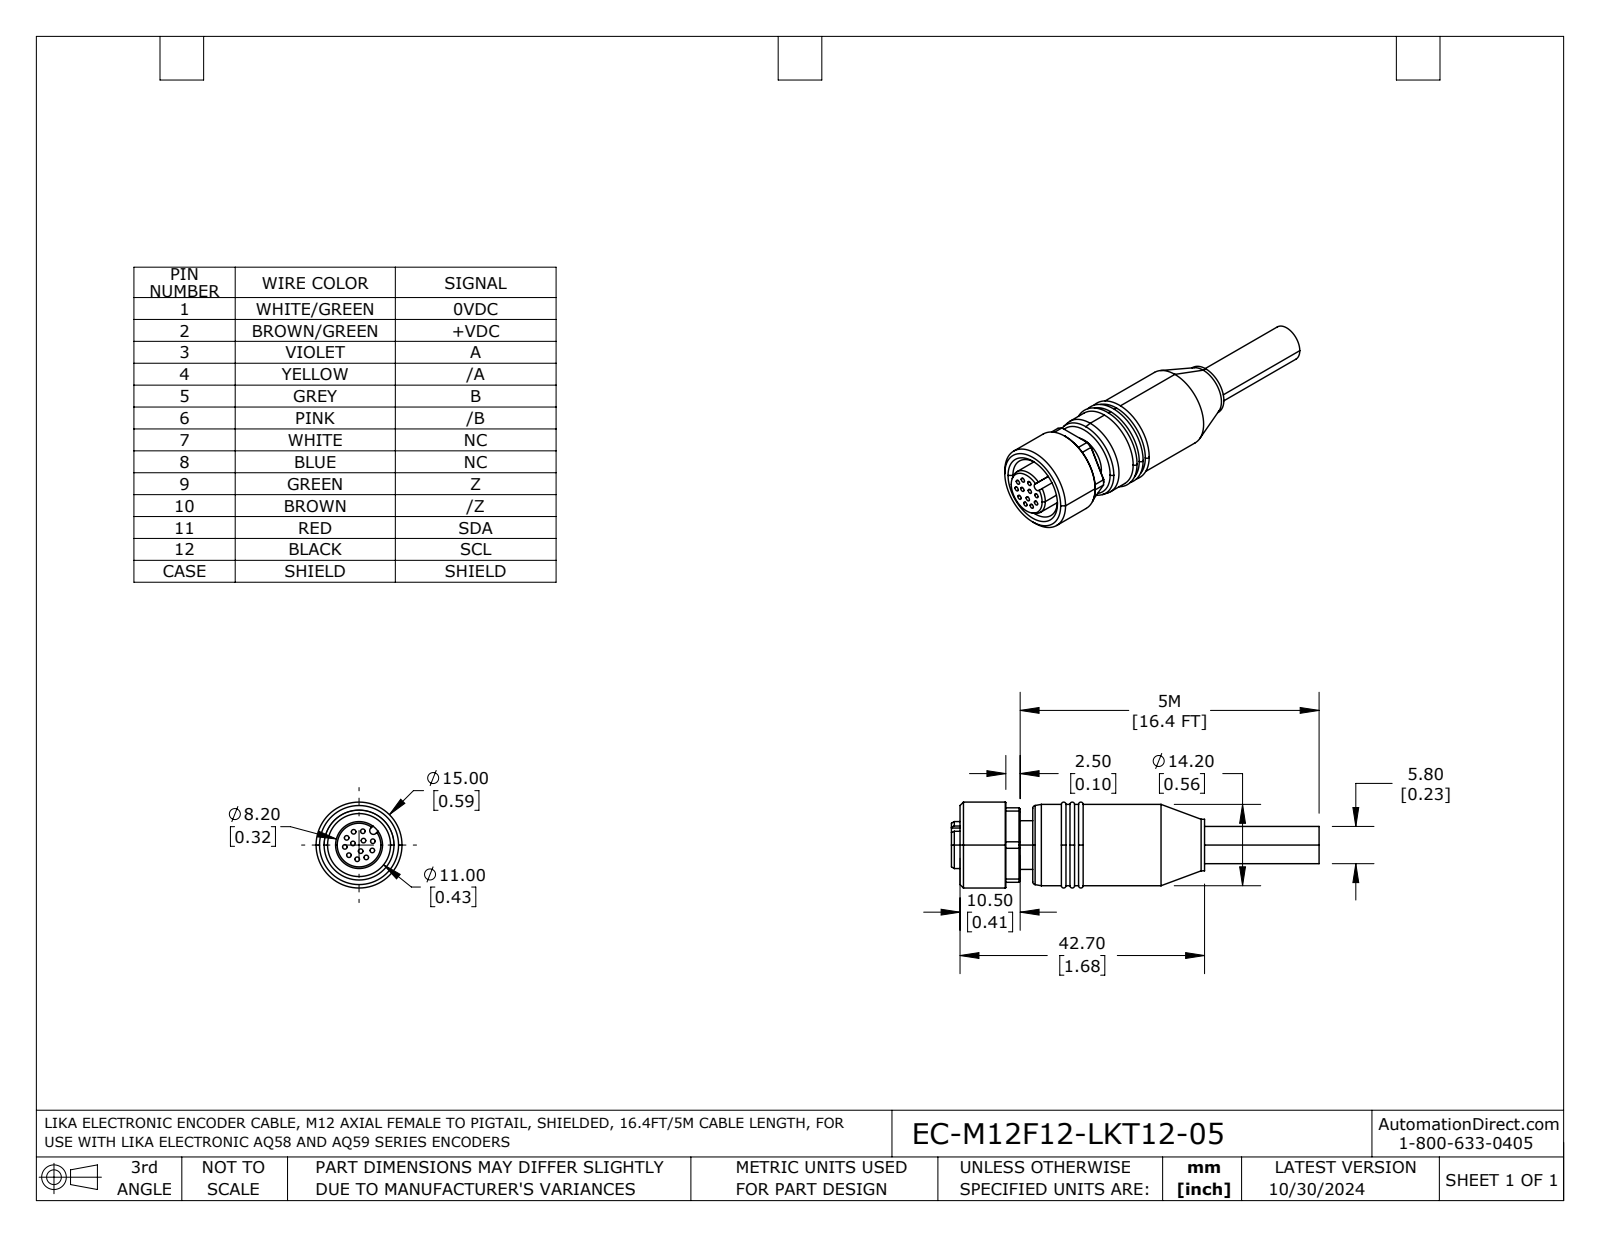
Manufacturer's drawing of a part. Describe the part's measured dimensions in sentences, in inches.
The part is named "EC-M12F12-LKT12-05". Its 3-D file was written by "SolidWorks 2021 (AUTOMOTIVE_DESIGN)". It is 1 solid with 146 faces: 35 planar, 73 cylindrical and 38 other. Overall it measures 2.528 by 0.591 by 0.591 inches. Its volume is 0.404 cubic inches and its surface area 5.314 square inches. Round holes: 12 of diameter 0.031, 1 of diameter 0.433. Round bosses or shafts: 1 of diameter 0.591, 1 of diameter 0.559, 1 of diameter 0.354, 1 of diameter 0.335, 1 of diameter 0.323, 1 of diameter 0.256. Partial cylindrical surfaces (rounded edges, fillets, slot ends): 1 of radius 0.026, 1 of radius 0.283. The main face-to-face distances are 0.087, 0.512, 0.205, 0.118, 0.559, 0.472, 0.354, 1.969, 2.055, 2.173. The hole center spacings are 0.098, 0.063, 0.164, 0.12, 0.191, 0.196, 0.043, 0.181.
